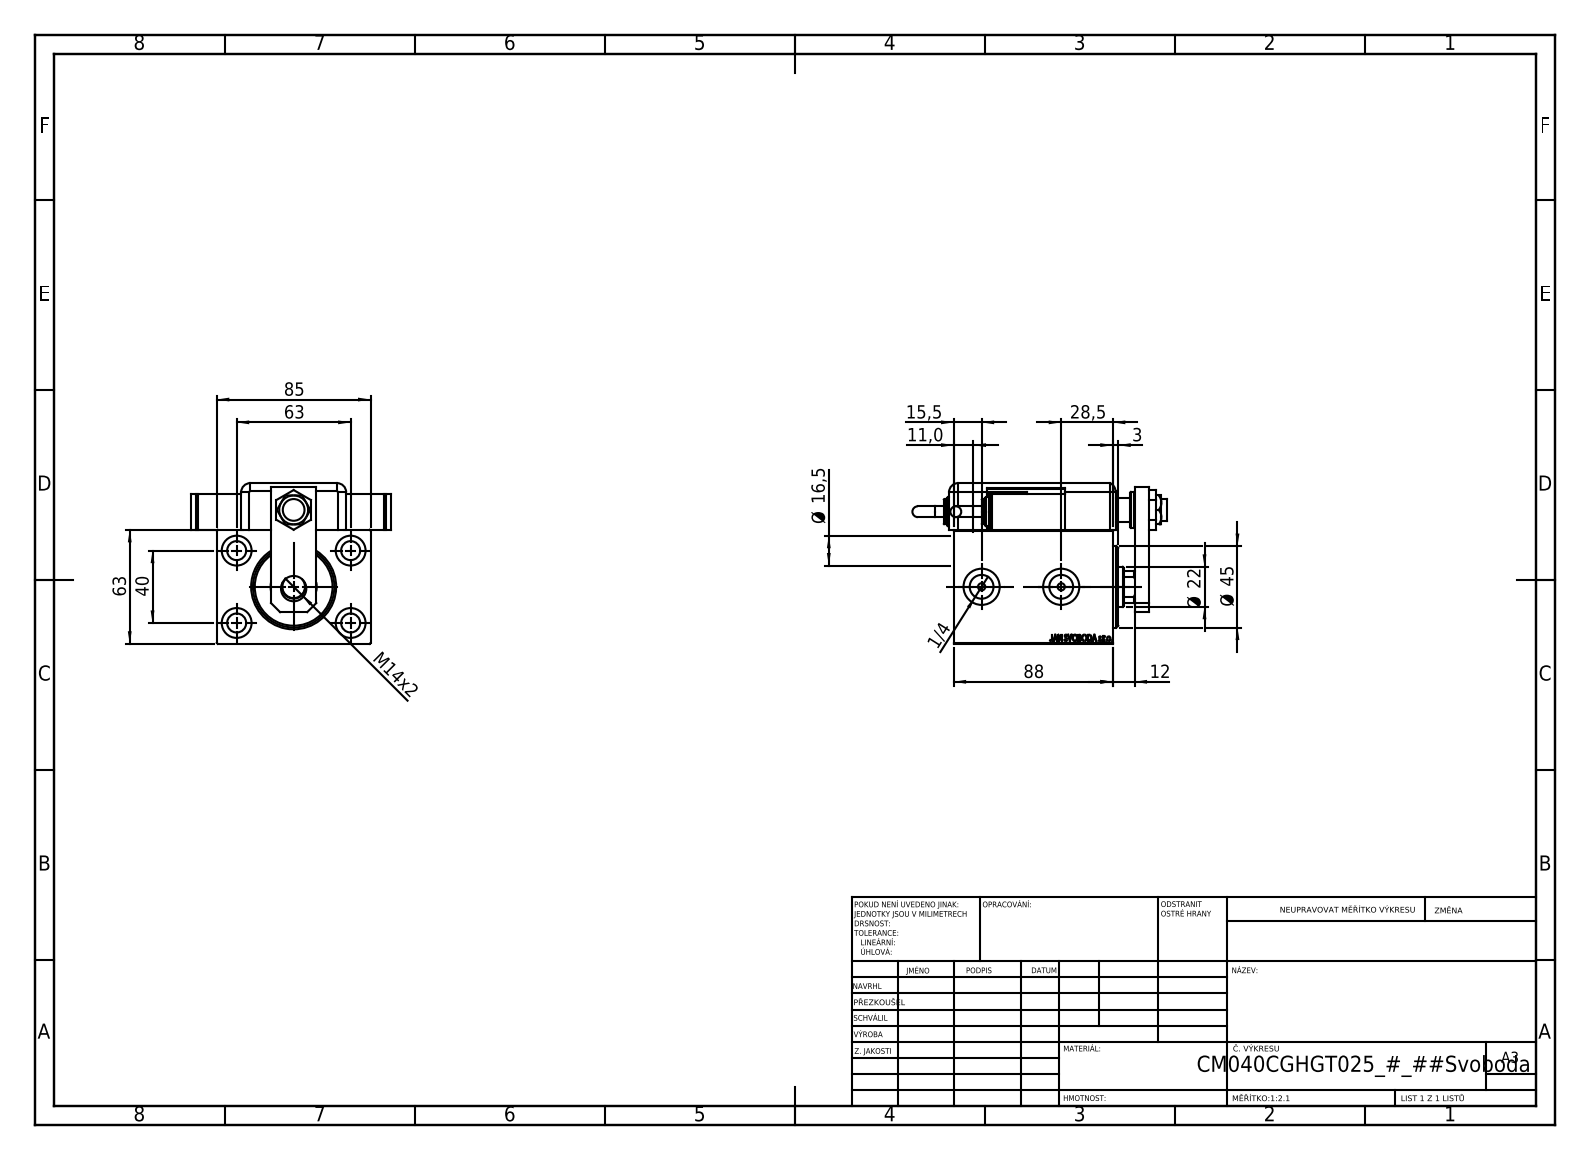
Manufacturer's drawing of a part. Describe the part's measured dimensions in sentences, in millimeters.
The part is named "TYC; ZARAZKA_Q; V450CM_C_VCP; NUT_D19 (+7 more)". Its 3-D file was written by "SolidWorks 2019 (CONFIG_CONTROL_DESIGN)". It is 13 solids with 1246 faces: 614 planar, 115 cylindrical and 517 other. Overall it measures 140.46 by 111 by 88.8 millimeters. Its volume is 542 356 cubic millimeters and its surface area 127 781 square millimeters. Round holes: 4 of diameter 4, 4 of diameter 10.5, 4 of diameter 16.5, 2 of diameter 8, 2 of diameter 13.16, 2 of diameter 14, 2 of diameter 20, 1 of diameter 12, 1 of diameter 12.5, 1 of diameter 13, 1 of diameter 22, 1 of diameter 25.5. Round bosses or shafts: 3 of diameter 20, 2 of diameter 16, 2 of diameter 14, 2 of diameter 6. Partial cylindrical surfaces (rounded edges, fillets, slot ends): 9 of radius 5, 1 of radius 10, 1 of radius 10.5. The main face-to-face distances are 3, 63, 13.5, 85, 12, 83, 10.5, 20, 88, 1.5. The hole center spacings are 37.31, 36.79, 37.86, 38.71, 40, 63, 69.99, 74.63.
